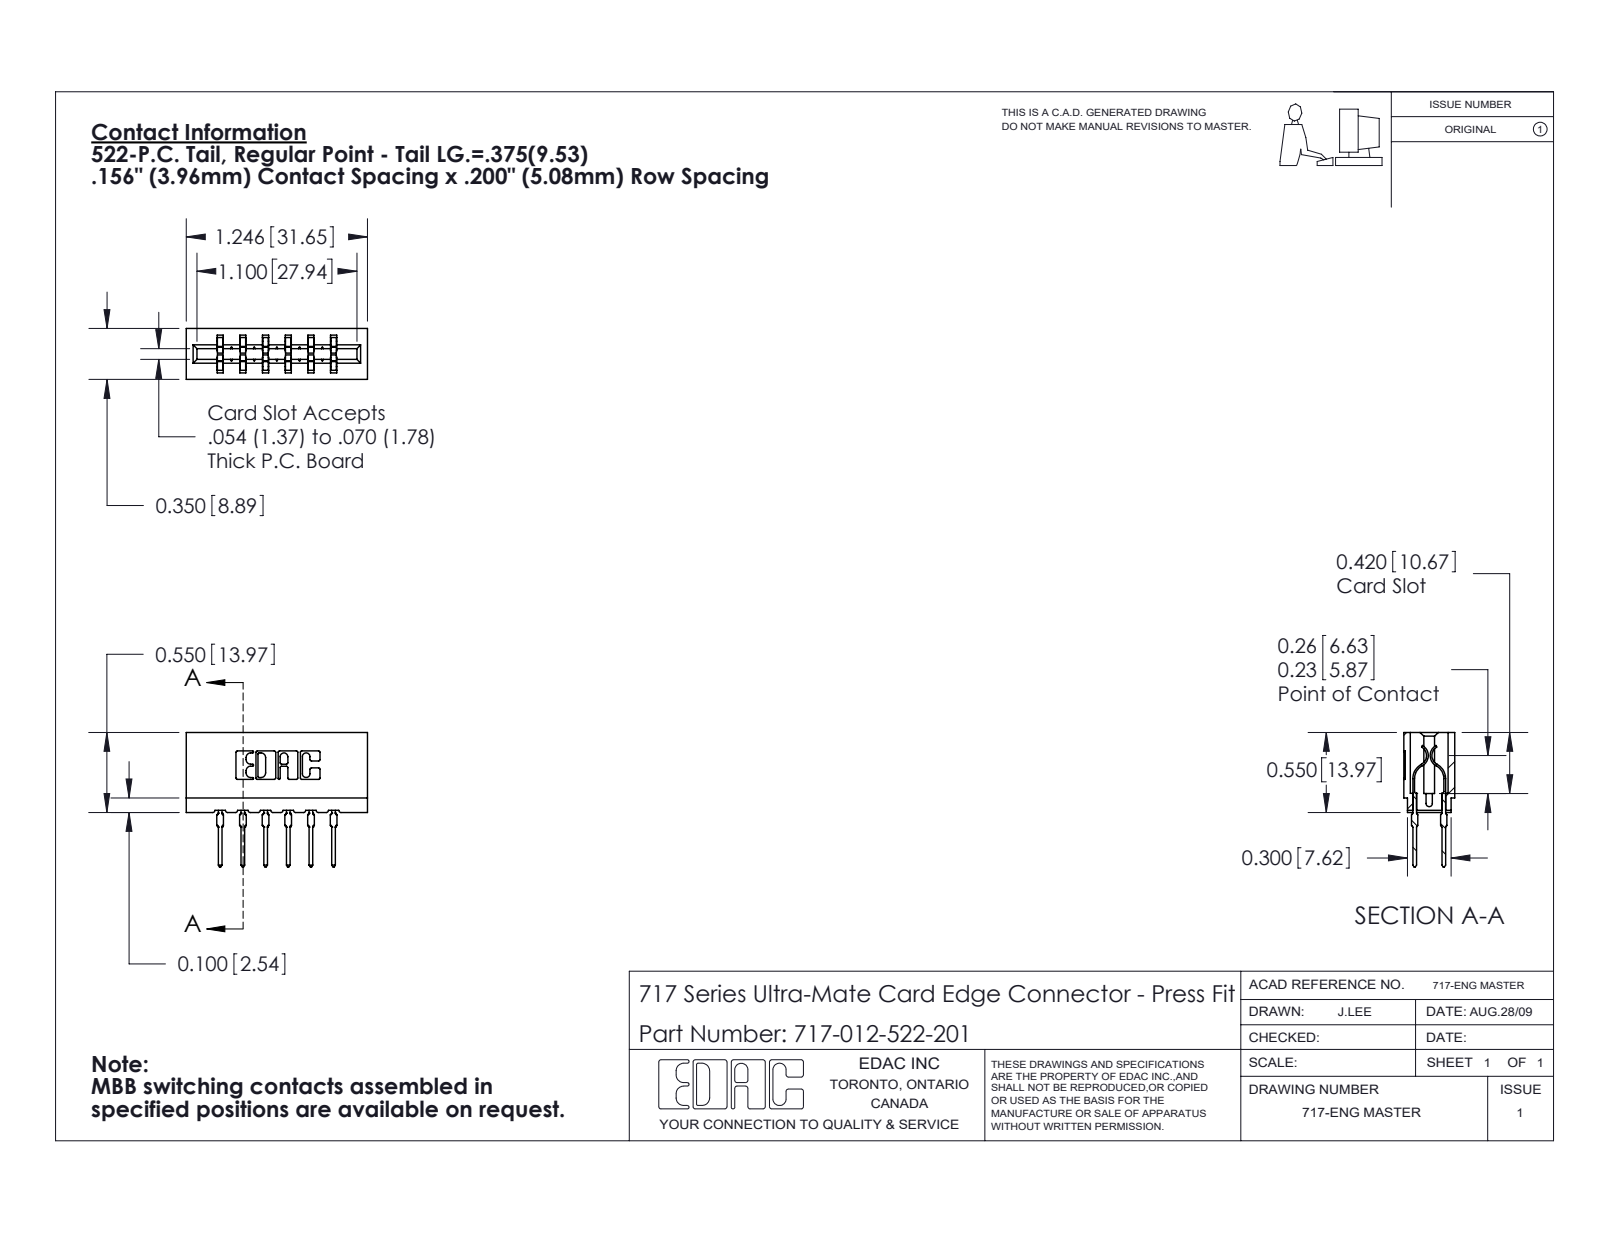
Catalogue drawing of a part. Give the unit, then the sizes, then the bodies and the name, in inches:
Units: inches
Overall size (bounding box): 1.246 × 0.924 × 0.35
Partial cylindrical surfaces — rounded edges, fillets, slot ends (radius × count): R0.021 ×24, R0.01 ×22, R0.015 ×12, R0.005 ×8, R0.011 ×8, R0.007 ×6, R0.031 ×6, R0.026 ×3
Main face-to-face distances: 0.212, 0.156, 0.138, 0.35, 0.198, 0.312, 0.624, 0.312, 0.042, 0.468
Volume: 0.177 in³ · Surface area: 6.21 in²
Bodies: 13 solids, 1174 faces (612 planar, 250 cylindrical, 312 other)
Part name (STEP PRODUCT): 745-292-001_522; 717 Part_Insulator Option - 06; 717-012-522-201
STEP written by: SolidWorks 2020 (CONFIG_CONTROL_DESIGN)
